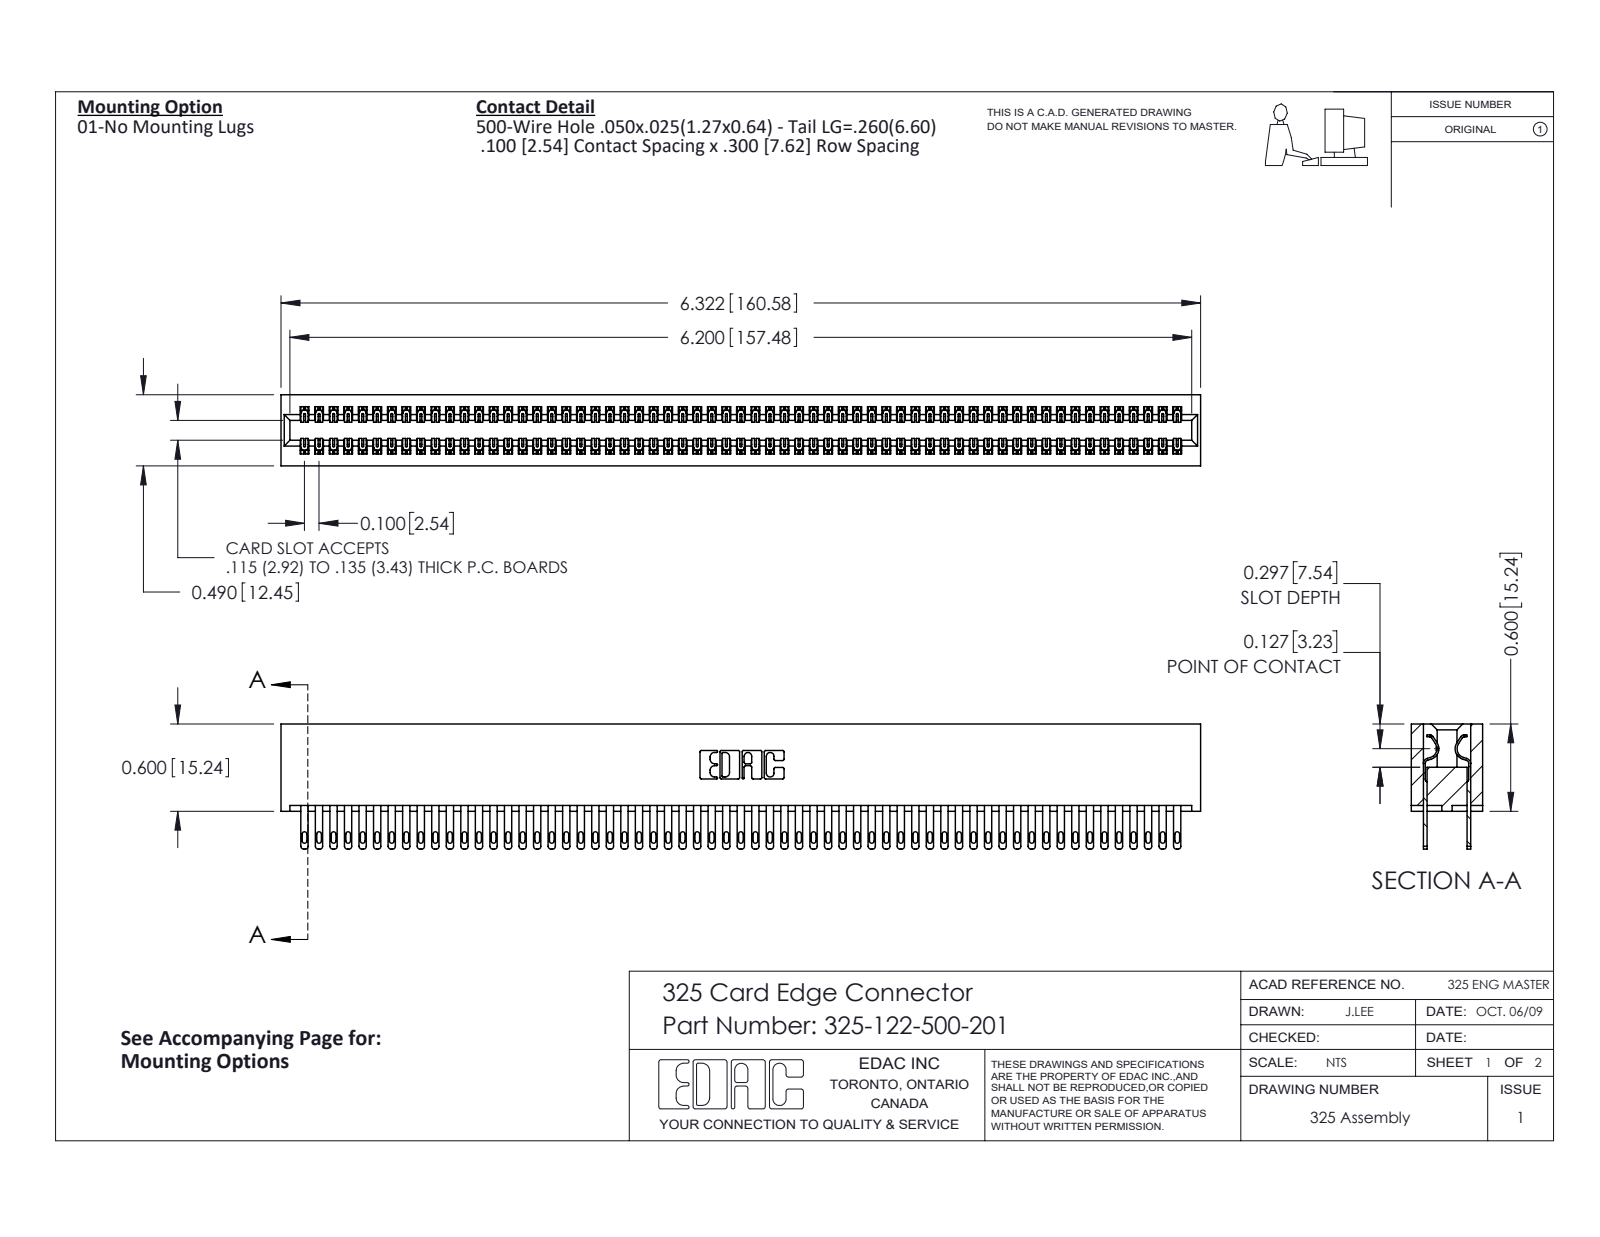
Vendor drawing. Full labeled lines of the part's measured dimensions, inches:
Part name (STEP PRODUCT): 325-292-001_325-293-100; 325 Part_Lugless; 325-122-500-201
STEP written by: SolidWorks 2016 (CONFIG_CONTROL_DESIGN)
Units: inches
Bodies: 123 solids, 5962 faces (3726 planar, 2236 cylindrical, 0 other)
Overall size (bounding box): 6.322 × 0.86 × 0.49
Volume: 1.335 in³ · Surface area: 44.75 in²
Partial cylindrical surfaces — rounded edges, fillets, slot ends (radius × count): R0.006 ×183, R0.016 ×122, R0.02 ×122, R0.01 ×22, R0.007 ×6, R0.031 ×6, R0.026 ×3, R0.014 ×2
Main face-to-face distances: 0.083, 0.407, 0.3, 0.107, 0.383, 0.025, 0.325, 0.49, 0.275, 0.263
